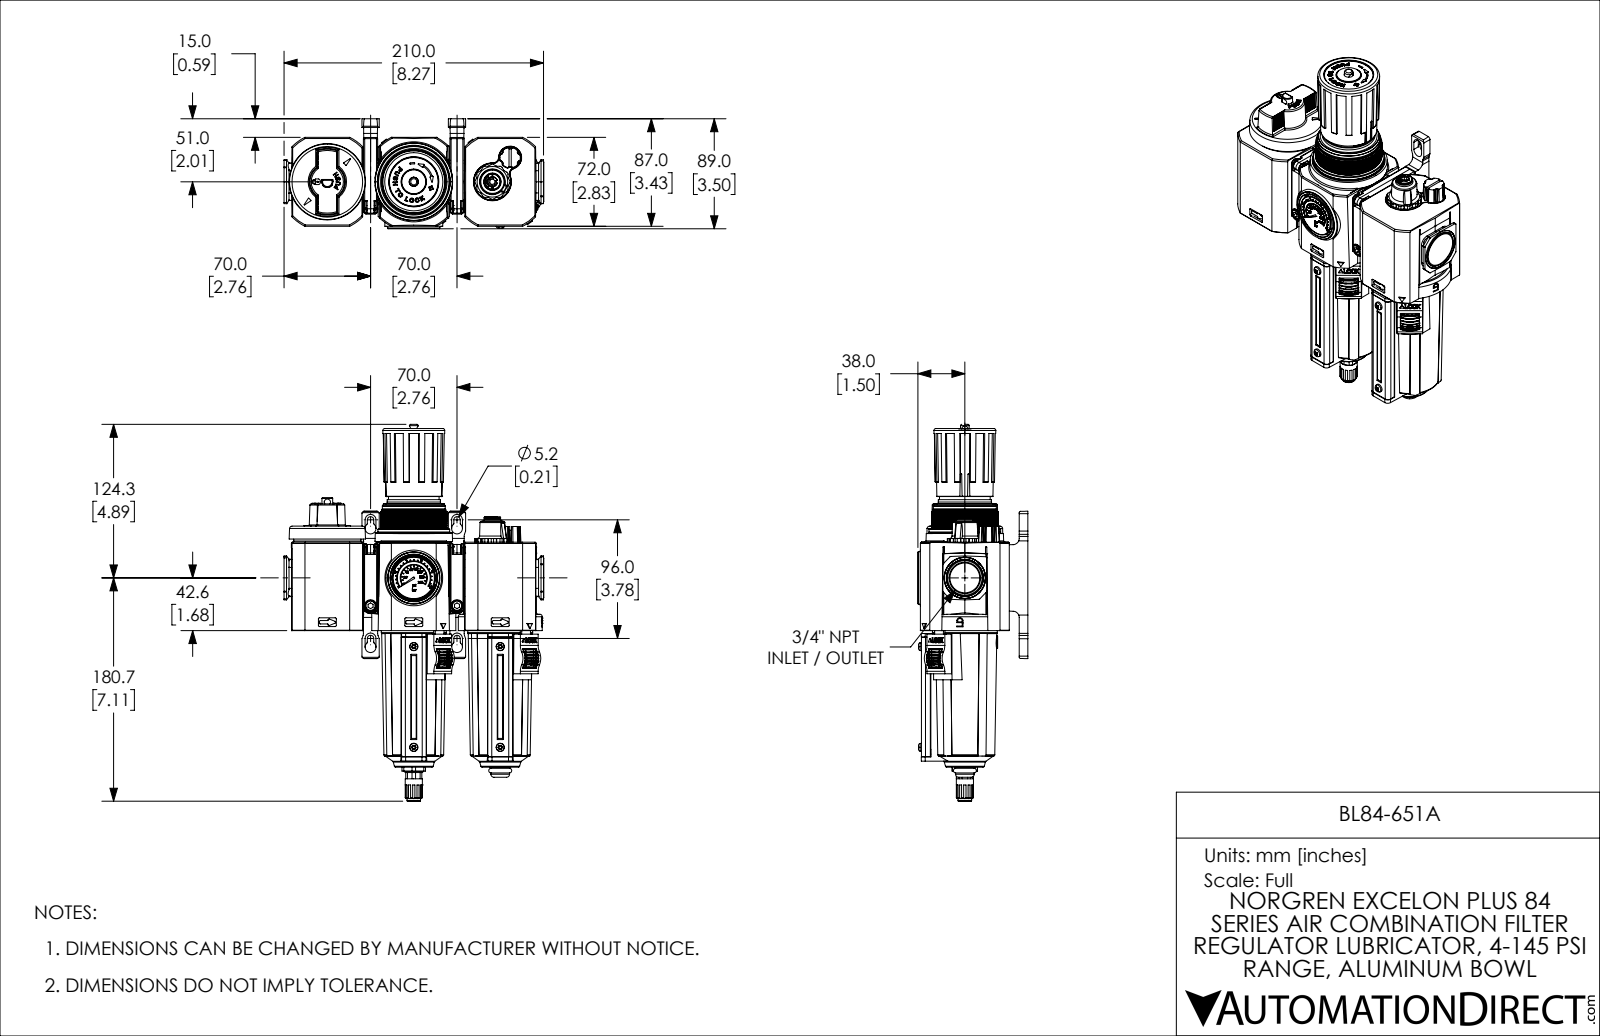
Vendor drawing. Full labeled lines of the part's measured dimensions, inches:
Part name (STEP PRODUCT): BL84-651A
STEP written by: SolidWorks 2021 (CONFIG_CONTROL_DESIGN)
Units: inches
Bodies: 21 solids, 5385 faces (2231 planar, 2172 cylindrical, 982 other)
Overall size (bounding box): 12.005 × 8.278 × 3.504
Volume: 90.88 in³ · Surface area: 572 in²
Round holes (diameter × count): ⌀0.112 ×4, ⌀0.22 ×3, ⌀0.163 ×2, ⌀0.177 ×2, ⌀0.197 ×2, ⌀0.335 ×2, ⌀0.633 ×2, ⌀2.461 ×2, ⌀0.039 ×1, ⌀0.059 ×1, ⌀0.126 ×1, ⌀0.246 ×1
Round bosses / shafts (diameter × count): ⌀0.213 ×4, ⌀0.197 ×4, ⌀2.122 ×2, ⌀2.067 ×2, ⌀2.018 ×2, ⌀1.959 ×2, ⌀1.953 ×2, ⌀0.399 ×2
Partial cylindrical surfaces — rounded edges, fillets, slot ends (radius × count): R0.039 ×138, R0.03 ×74, R0.02 ×64, R0.028 ×56, R0.01 ×47, R0.079 ×44, R0.004 ×30, R0.012 ×27
Main face-to-face distances: 2.756, 5.512, 2.753, 2.457, 2.835, 0.378, 0.404, 2.411, 2.913, 2.815
Hole centre spacings: 2.756, 2.895, 2.157, 4.386, 5.235, 0.157, 0.522, 0.856
